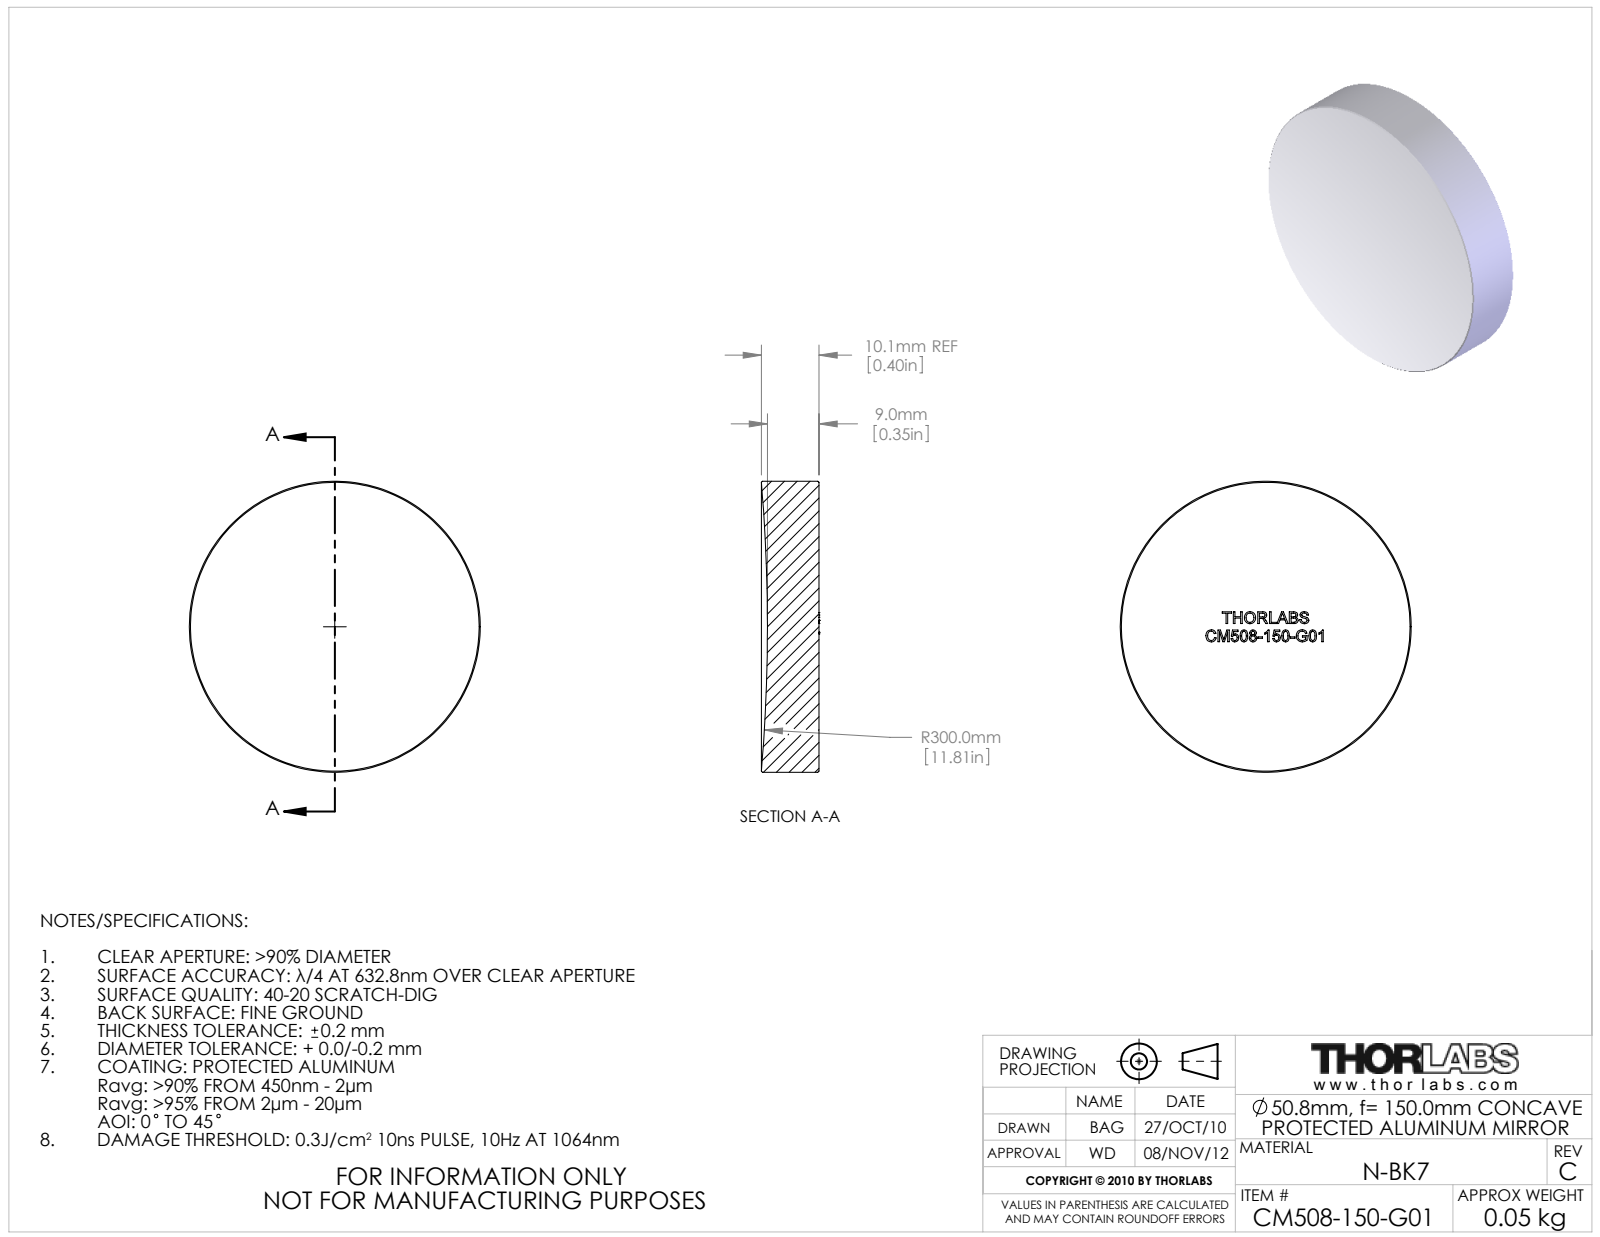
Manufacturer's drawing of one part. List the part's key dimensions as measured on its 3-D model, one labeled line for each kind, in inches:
Part name (STEP PRODUCT): 12015-E0W
STEP written by: SolidWorks 2009 (AUTOMOTIVE_DESIGN)
Units: inches
Bodies: 1 solid, 281 faces (144 planar, 2 cylindrical, 135 other)
Overall size (bounding box): 2 × 2 × 0.396
Volume: 1.179 in³ · Surface area: 8.721 in²
Round bosses / shafts (diameter × count): ⌀2 ×1
Main face-to-face distances: 0.218, 0.273, 0.038, 0.081, 0.067, 0.206, 0.055, 0.078, 0.116, 0.101
